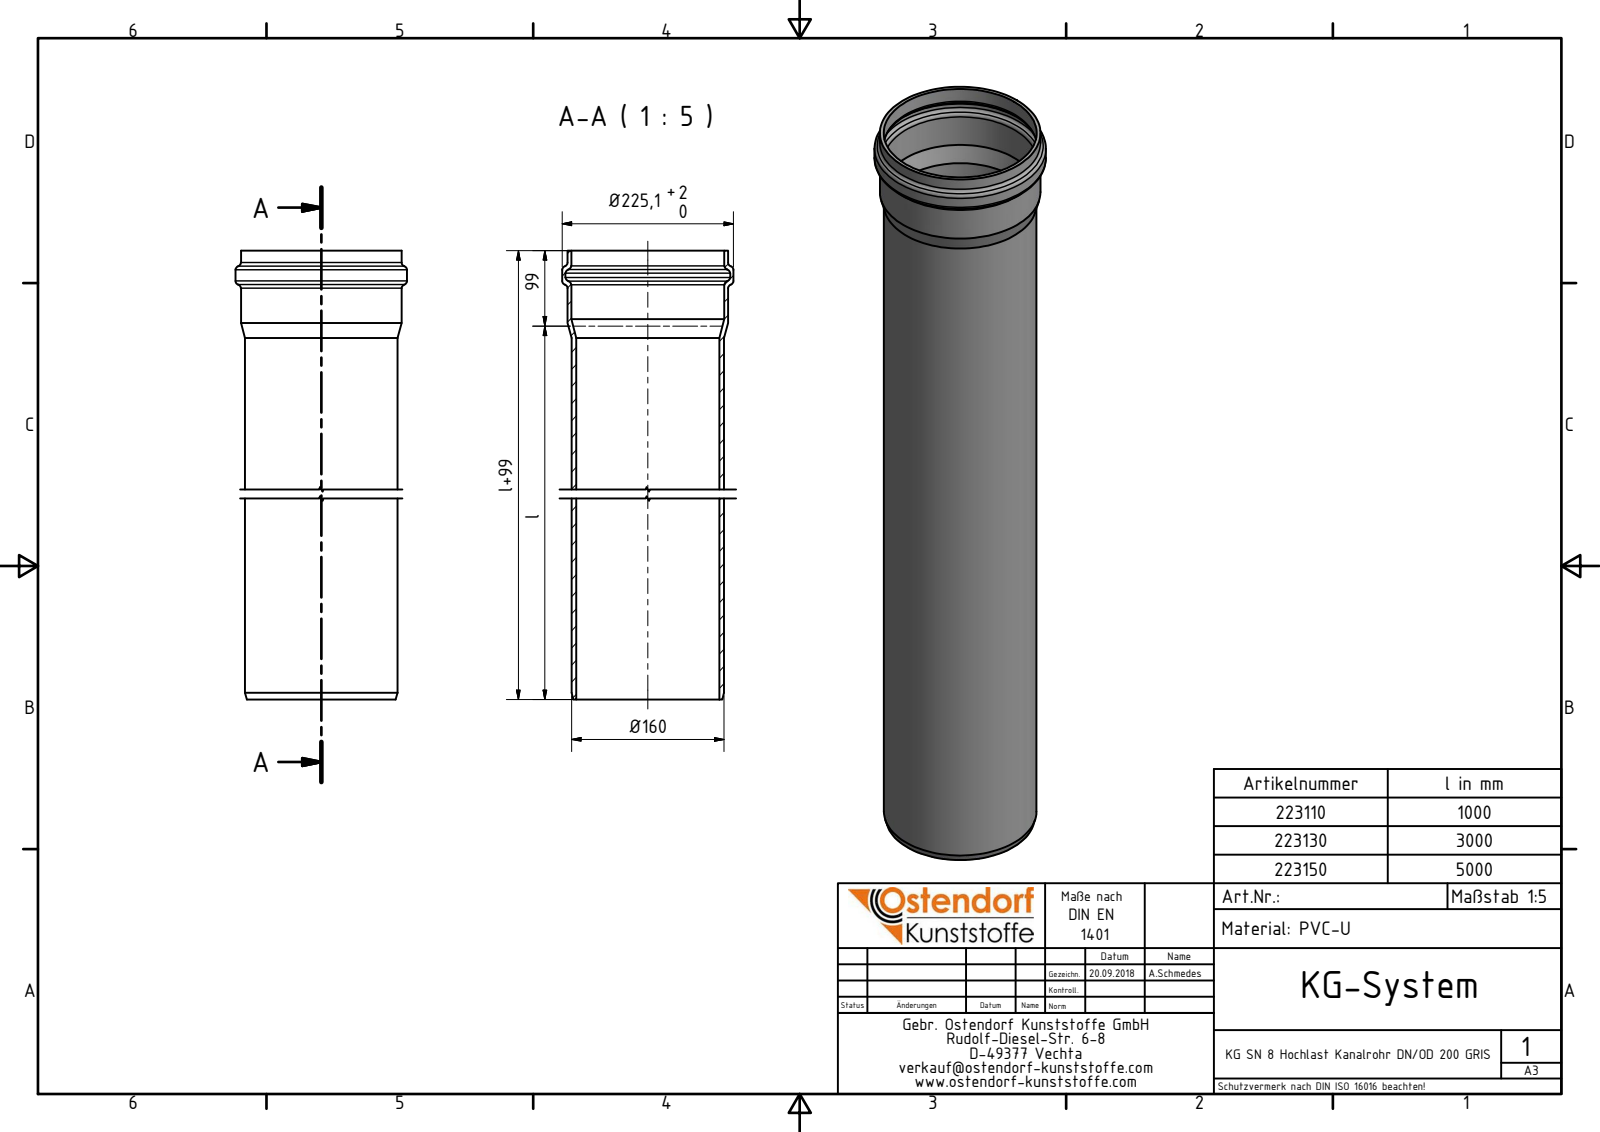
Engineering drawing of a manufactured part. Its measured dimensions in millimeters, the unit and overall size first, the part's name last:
Units: millimetres
Overall size (bounding box): 5099 × 225.1 × 225.1
Round holes (diameter × count): ⌀187.65 ×1, ⌀200.85 ×1, ⌀216.3 ×1
Round bosses / shafts (diameter × count): ⌀225.1 ×1, ⌀210.85 ×1, ⌀200.25 ×1
Main face-to-face distances: 5099
Volume: 19 550 000 mm³ · Surface area: 6 239 000 mm²
Bodies: 1 solid, 21 faces (2 planar, 8 cylindrical, 11 other)
Part name (STEP PRODUCT): 243150 KGEM Passlängen SN 8 DN_OD 200x5000 GRIS
STEP written by: Autodesk Inventor 2016 (AUTOMOTIVE_DESIGN)
